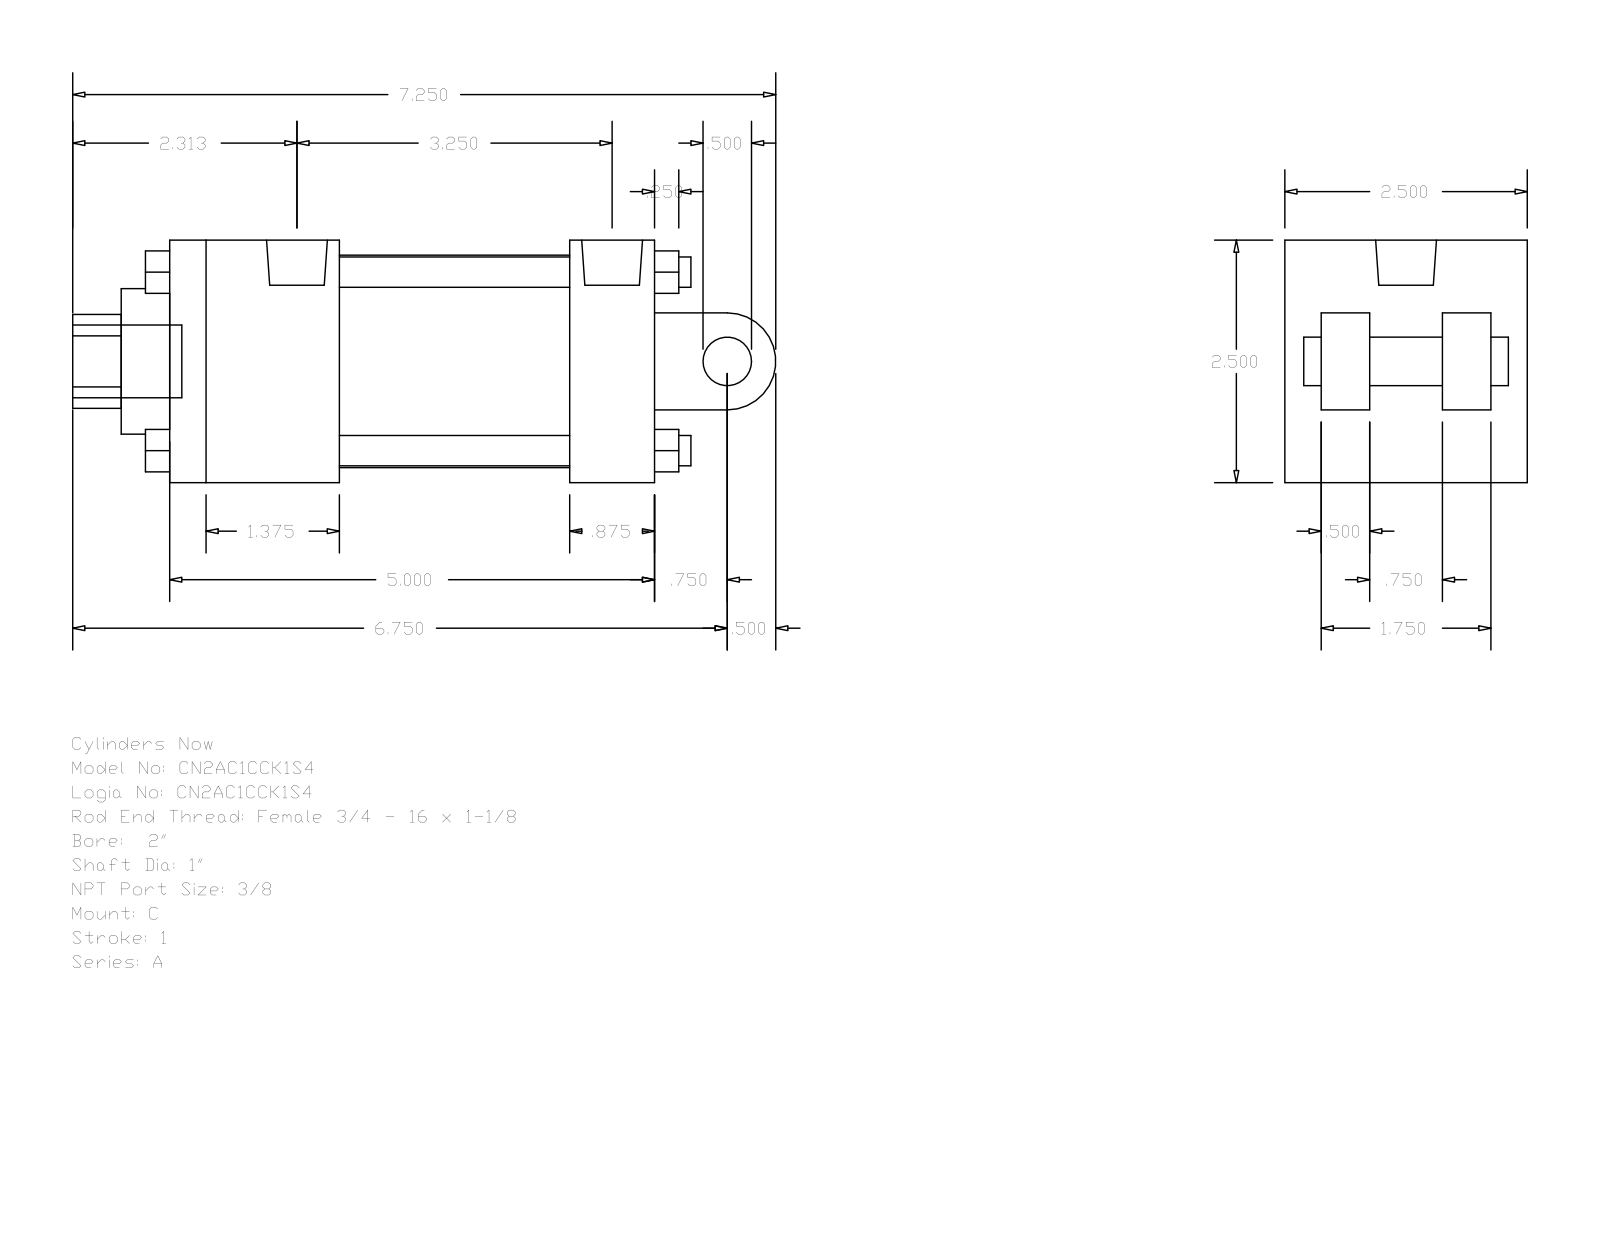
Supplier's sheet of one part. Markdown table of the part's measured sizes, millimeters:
| quantity | value |
| --- | --- |
| part name | A_C__0200_1 |
| STEP written by | GSSL Pune (CONFIG_CONTROL_DESIGN) |
| units | millimeters |
| bodies | 0 solids, 135 faces (102 planar, 33 cylindrical, 0 other) |
| overall size | 184.15 × 63.5 × 63.5 |
| round holes (diameter × count) | 5.56 × 2, 15.93 × 1, 25.4 × 1, 38.1 × 1, 55.63 × 1 |
| round bosses / shafts (diameter × count) | 7.94 × 4, 5.56 × 2, 19.05 × 1, 15.93 × 1, 12.7 × 1 |
| partial cylindrical surfaces (radius × count) | 12.29 × 1, 12.7 × 1 |
| main face-to-face distances | 63.5, 22.22, 127, 44.45, 12.7, 9.52, 41.28, 82.55, 104.78, 60.33 |
| hole center spacings | 3.98 |
